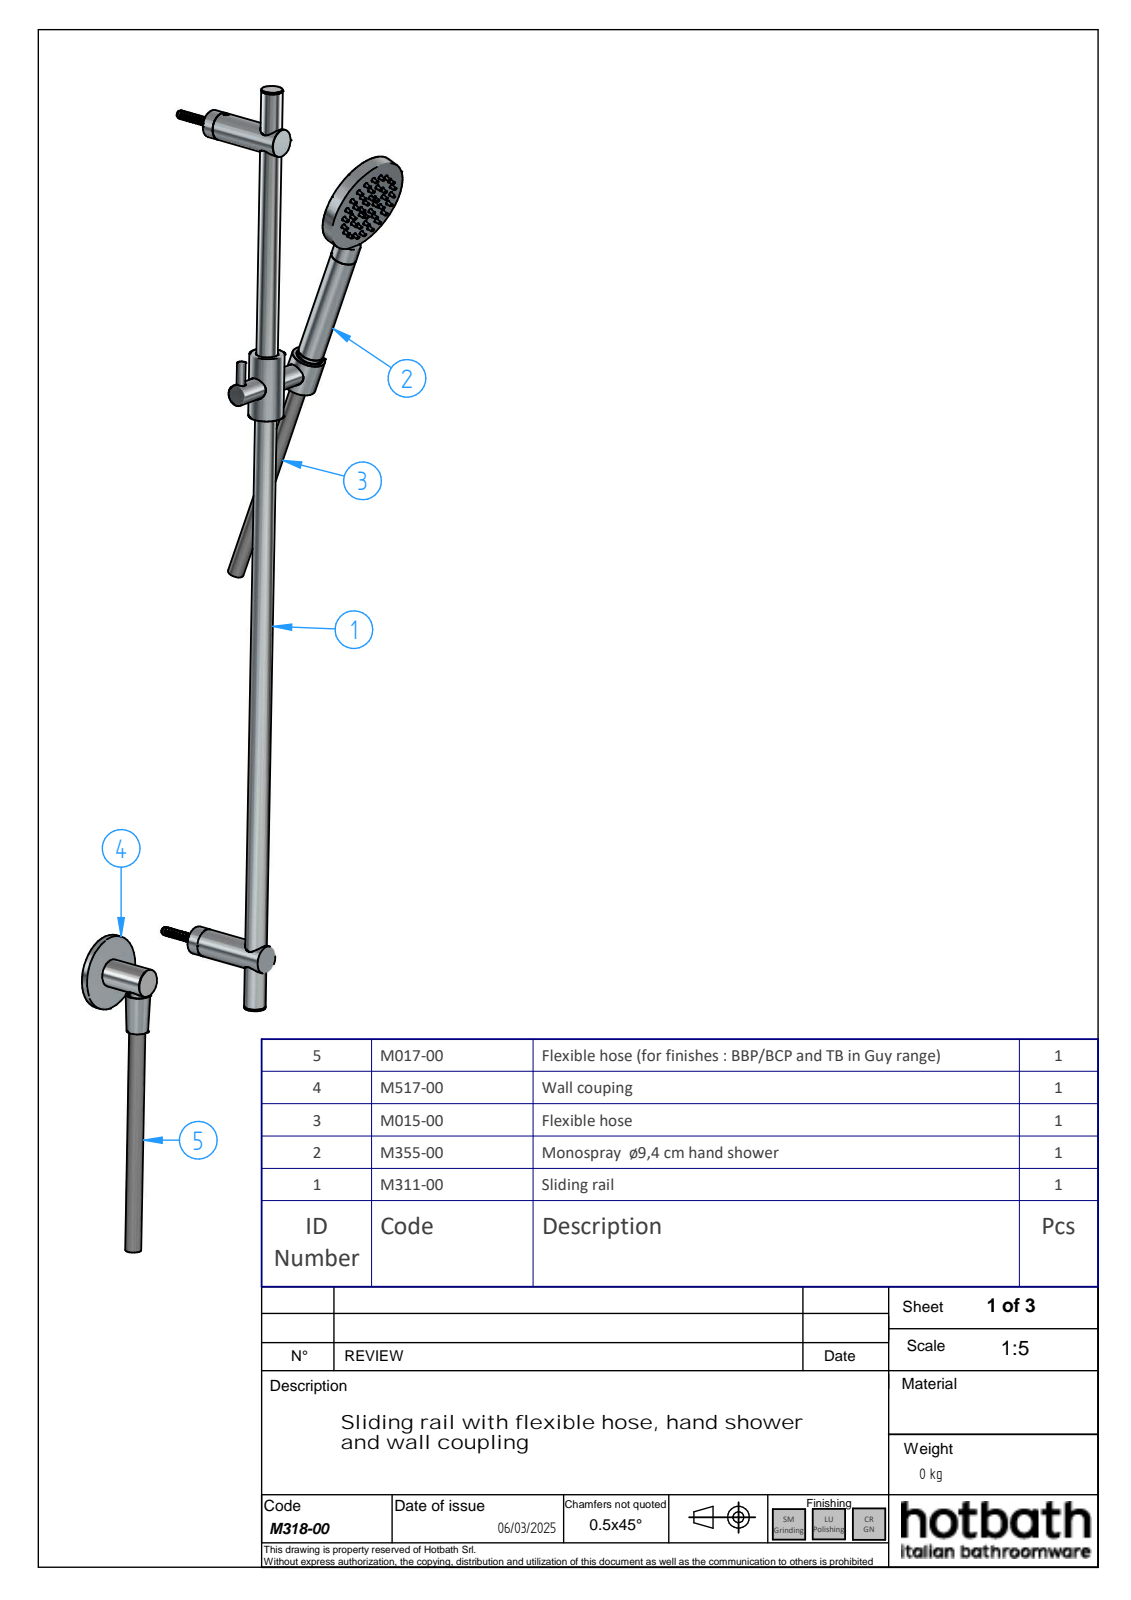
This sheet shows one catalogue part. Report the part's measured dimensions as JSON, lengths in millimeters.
{"part_name": "M318-00; M311-00 rel3_oa_0; M307-001 variante testa piatta_oa_1; M307-11 (+8 more)", "step_written_by": "Solid Edge (AUTOMOTIVE_DESIGN)", "units": "millimeters", "bodies": {"solids": 27, "faces": 1839, "planar": 452, "cylindrical": 465, "other": 922}, "overall_size": [1112.73, 267.35, 176.72], "volume_mm3": 352919, "surface_area_mm2": 284198, "round_holes": [[4.4, 40], [2.4, 10], [2.5, 6], [6, 3], [18.63, 3], [20, 3], [3.2, 2], [3.24, 2], [4.13, 2], [4.2, 2], [4.92, 2], [8, 2]], "round_bosses_or_shafts": [[26, 3], [24, 2], [20.95, 2], [19.5, 2], [4, 2], [94, 1], [73.7, 1], [70, 1]], "partial_cylinders_radius": [[0.2, 50], [2, 10], [9, 10], [0.46, 4], [0.5, 4], [6, 4], [0.11, 3], [0.12, 3]], "face_to_face_distances": [1.5, 8.2, 9.7, 3, 6.7, 6.3, 1.9, 4.3, 81.2, 79.3], "hole_center_spacings": [9.77, 66.59, 32, 37.62, 70.04, 10.01, 18.52, 28.53]}
